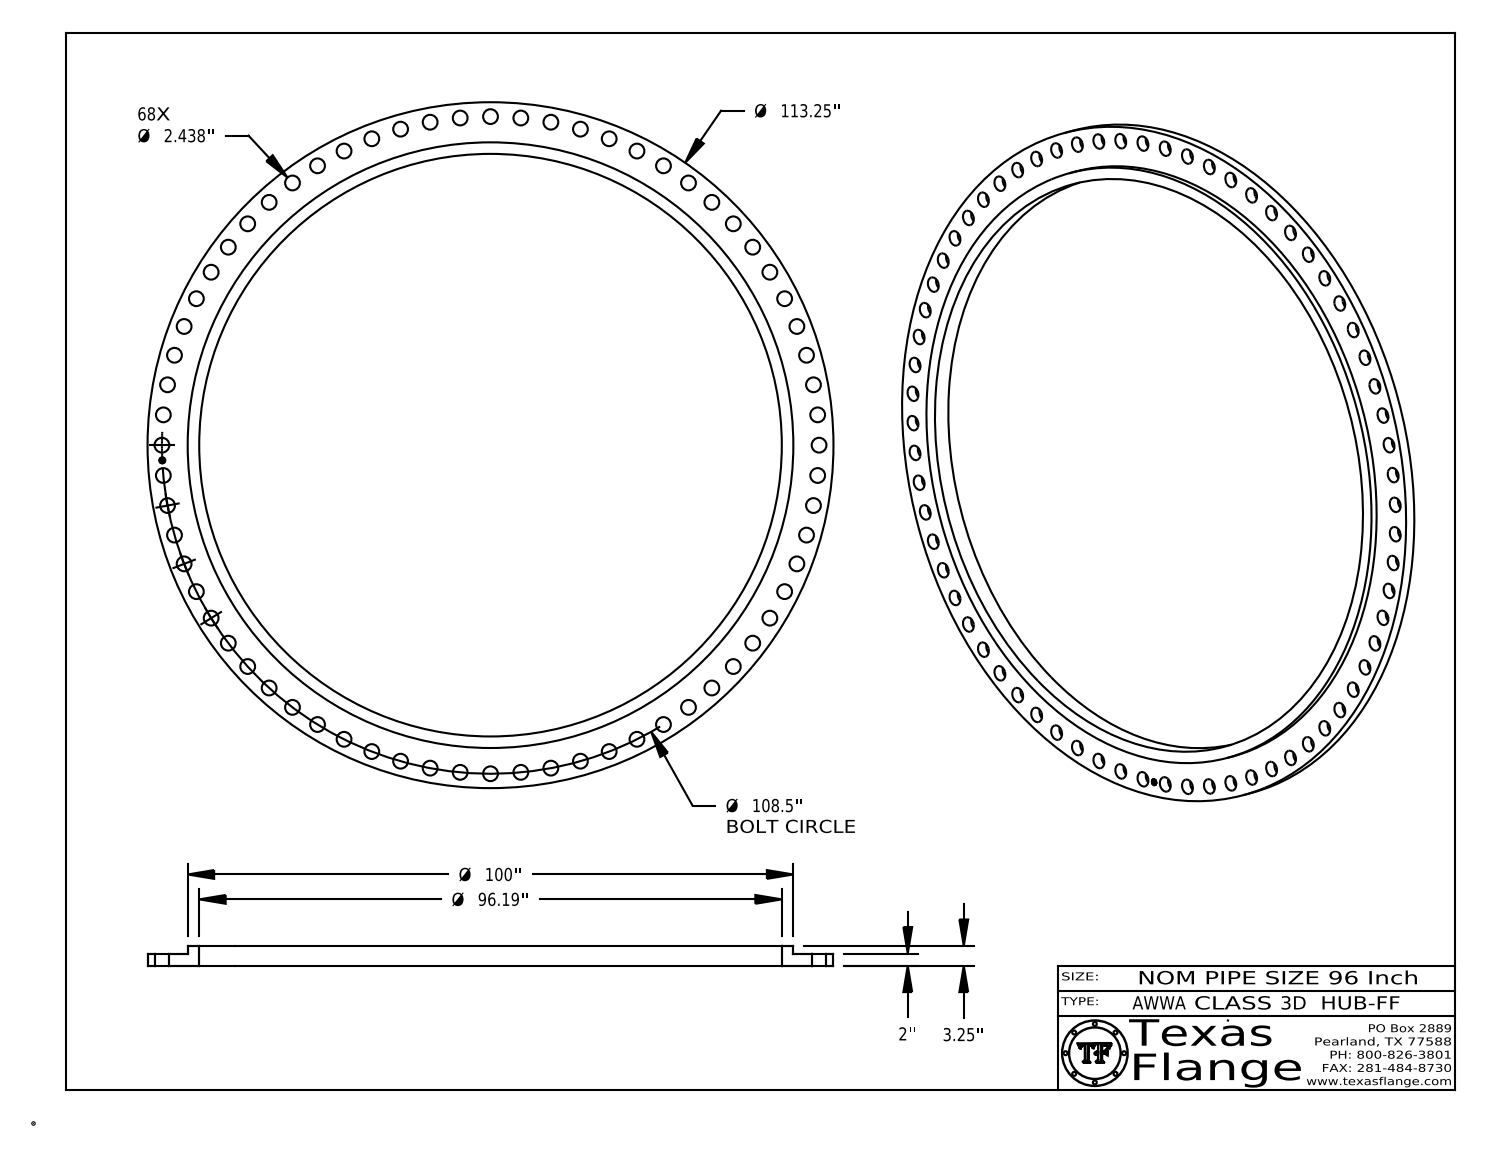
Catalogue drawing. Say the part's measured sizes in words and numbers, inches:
The part is named "AWWA Class 3D-HUB-FF". Its 3-D file was written by "CATIA V5 STEP AP214 (AUTOMOTIVE_DESIGN)". It is 1 solid with 530 faces: 368 planar, 162 cylindrical and 0 other. Overall it measures 113.25 by 113.25 by 3.25 inches. Its volume is 5 711 cubic inches and its surface area 8 106 square inches. Round holes: 68 of diameter 2.438, 1 of diameter 1, 1 of diameter 96.19. Round bosses or shafts: 8 of diameter 0.061, 1 of diameter 113.25, 1 of diameter 100, 1 of diameter 0.788. The main face-to-face distances are 2, 3.25, 1.25, 1.985, 0.015, 1.265, 0.298, 0.293, 0.054, 0.193. The hole center spacings are 54.25, 29.693, 5.011, 10.011, 14.99, 19.937, 39.195, 43.826.
